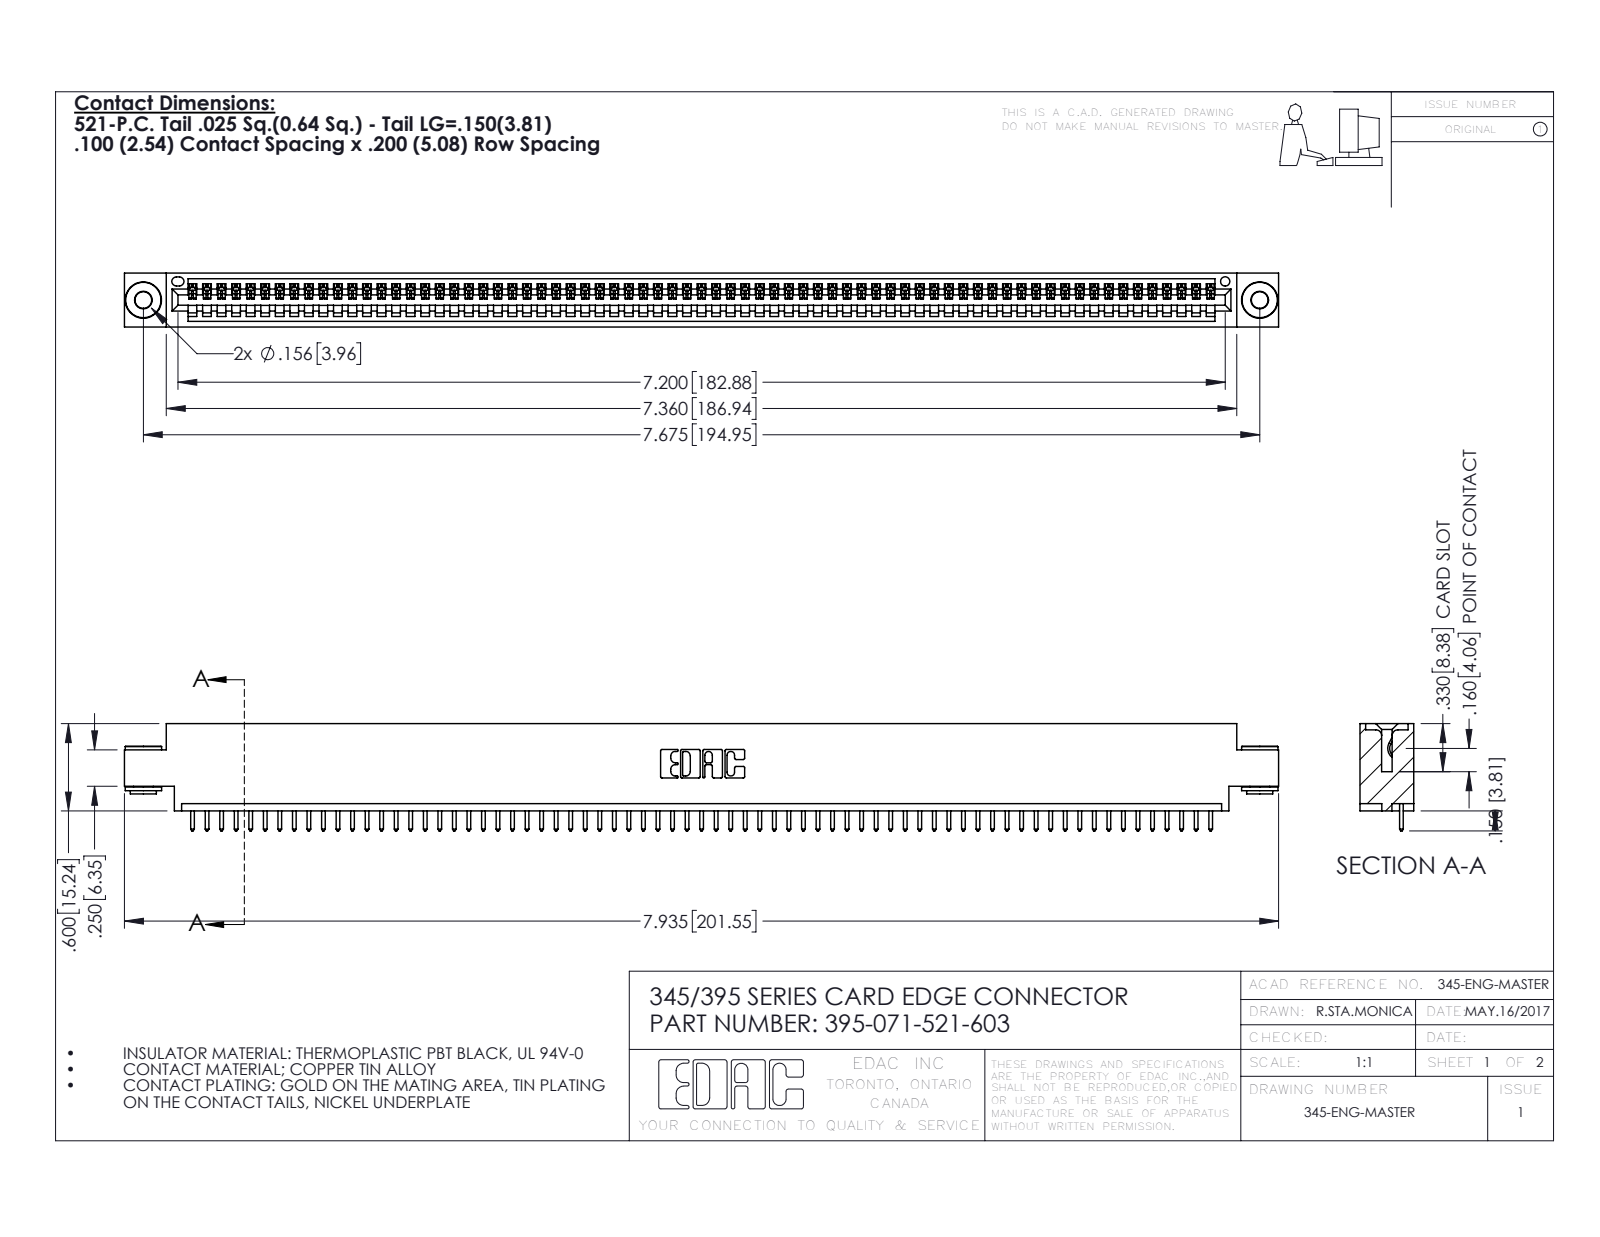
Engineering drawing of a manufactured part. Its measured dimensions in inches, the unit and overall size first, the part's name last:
Units: inches
Overall size (bounding box): 7.935 × 0.737 × 0.37
Round holes (diameter × count): ⌀0.116 ×2, ⌀0.156 ×2, ⌀0.064 ×1
Round bosses / shafts (diameter × count): ⌀0.25 ×2, ⌀0.18 ×2, ⌀0.136 ×2
Partial cylindrical surfaces — rounded edges, fillets, slot ends (radius × count): R0.006 ×142, R0.01 ×142, R0.01 ×22, R0.007 ×6, R0.031 ×6, R0.026 ×3, R0.031 ×2, R0.04 ×2
Main face-to-face distances: 0.072, 0.298, 0.37, 0.2, 0.098, 0.272, 0.025, 0.225, 0.175, 0.149
Hole centre spacings: 0.27, 7.439, 7.675
Volume: 1.165 in³ · Surface area: 39.23 in²
Bodies: 74 solids, 4286 faces (2934 planar, 1344 cylindrical, 8 other)
Part name (STEP PRODUCT): 345-292-001_345-293-121; 395-071-521-603; 345-250-002_345-250-002-102; 345 Part_0.170 Offset - 0.156 Dia-TH
STEP written by: SolidWorks 2016 (CONFIG_CONTROL_DESIGN)
